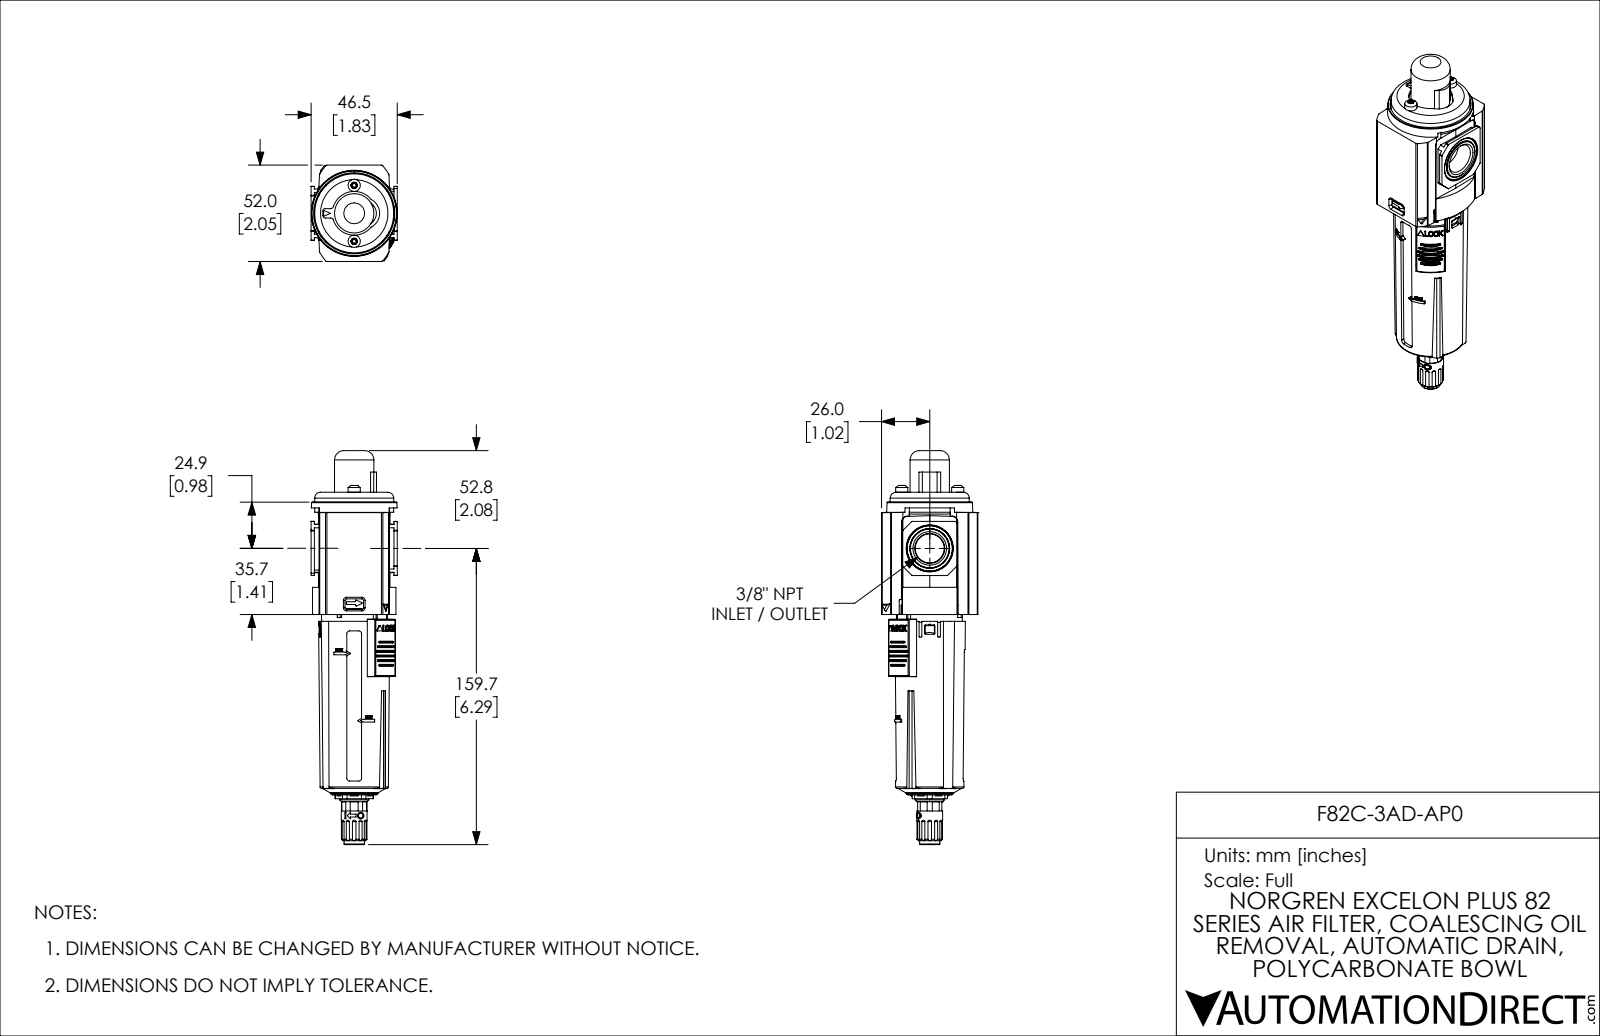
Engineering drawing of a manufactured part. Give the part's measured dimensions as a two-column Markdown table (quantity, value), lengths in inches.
| quantity | value |
| --- | --- |
| part name | F82C-3AD-AP0 |
| STEP written by | SolidWorks 2021 (CONFIG_CONTROL_DESIGN) |
| units | inches |
| bodies | 8 solids, 1263 faces (536 planar, 493 cylindrical, 234 other) |
| overall size | 8.367 × 2.047 × 1.831 |
| volume | 14.42 in³ |
| surface area | 93.74 in² |
| round holes (diameter × count) | 0.059 × 2, 0.079 × 2, 0.128 × 2, 0.173 × 2, 0.098 × 1, 0.259 × 1, 0.63 × 1 |
| round bosses / shafts (diameter × count) | 0.26 × 2, 0.157 × 2, 1.678 × 1, 1.524 × 1, 1.388 × 1, 1.356 × 1, 1.291 × 1, 1.257 × 1 |
| partial cylindrical surfaces (radius × count) | 0.02 × 78, 0.039 × 42, 0.012 × 11, 0.008 × 10, 0.01 × 10, 0.031 × 8, 0.036 × 8, 0.048 × 8 |
| main face-to-face distances | 0.059, 1.988, 2.047, 1.929, 1.896, 0.182, 1.352, 1.475, 0.123, 1.293 |
| hole center spacings | 0.797, 0.531, 0.594, 0.594, 1.189, 1.063, 1.188, 1.189 |
